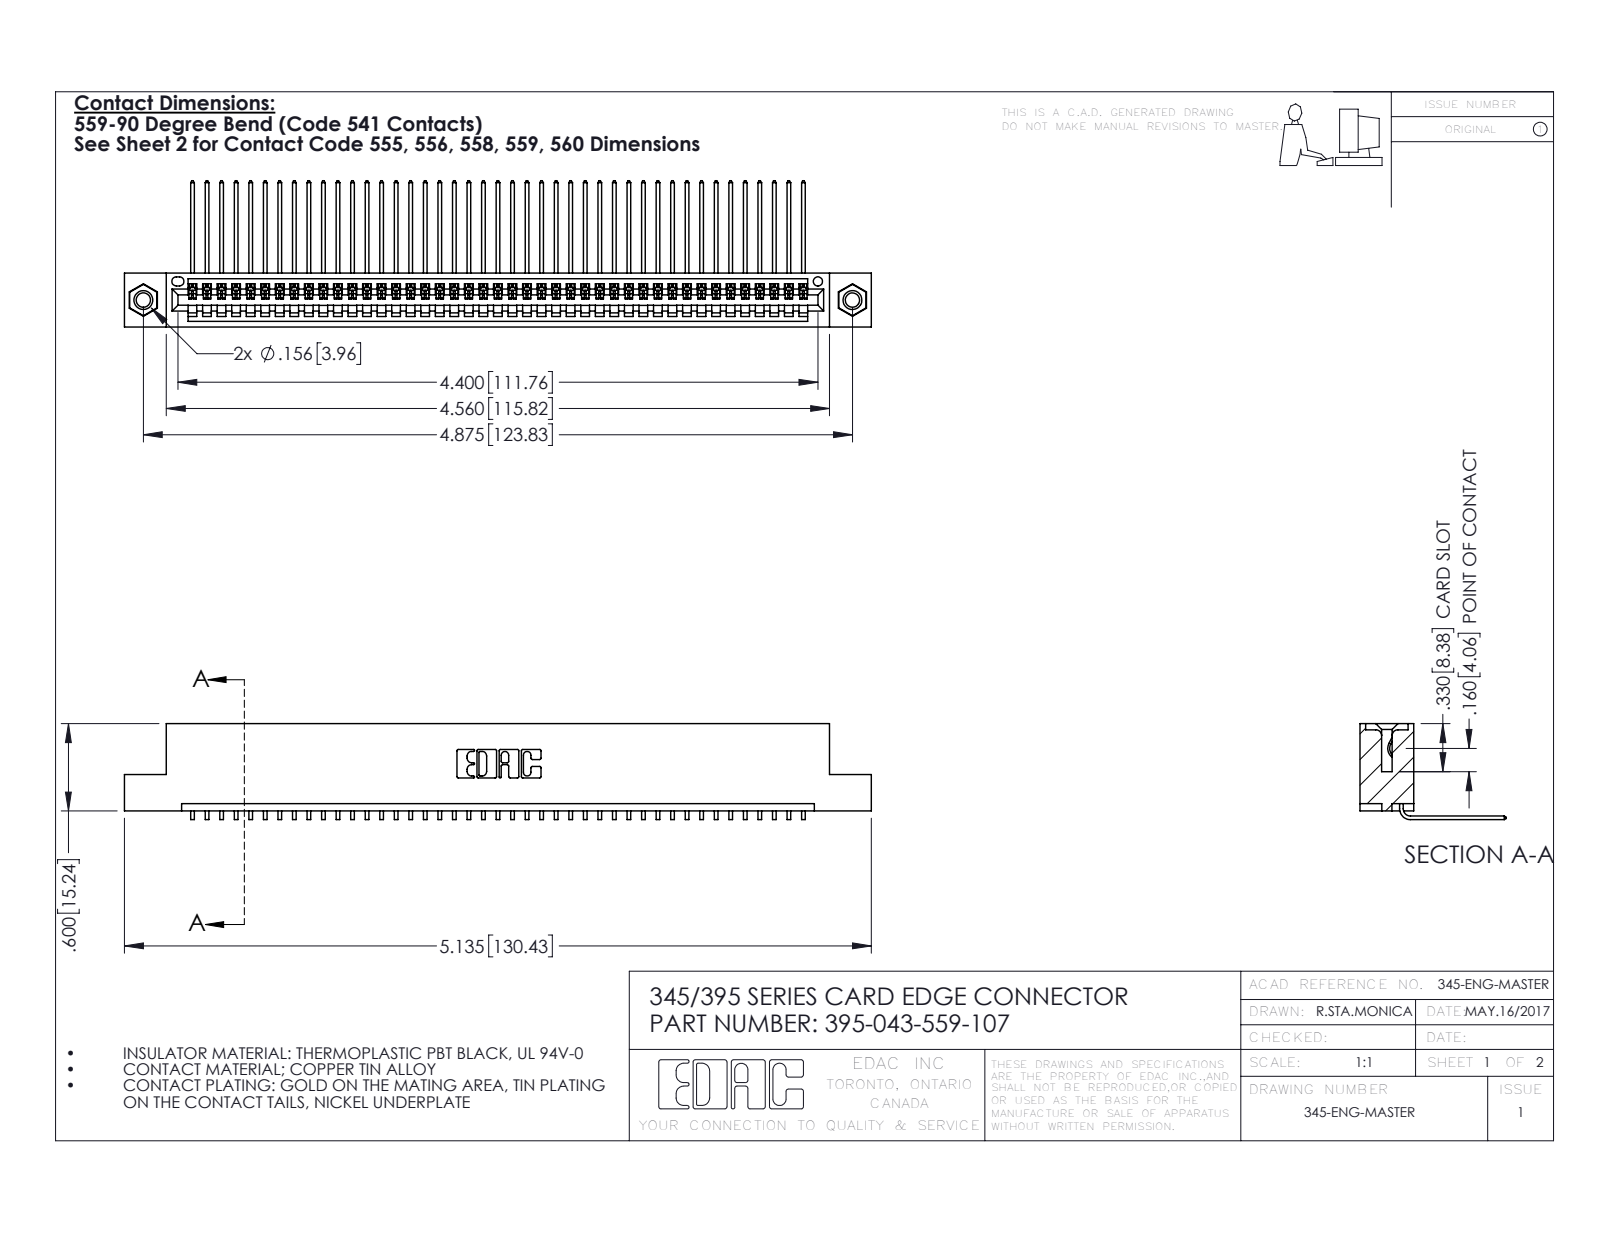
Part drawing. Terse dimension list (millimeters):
name: 345-250-001_345-250-005-103; 345-292-001_558 559 Tail - 1; 345 Part_Flush Mounting Lugs - 0.156 Dia-TI; 395-043-559-107
written by: SolidWorks 2016 (CONFIG_CONTROL_DESIGN)
unit: mm
bodies: 46 solids, 2766 faces (1918 planar, 832 cylindrical, 16 other)
size: 130.4 × 25.5 × 16.7
volume: 12 500 mm³; area: 17 540 mm²
holes: 2× ⌀2.5, 2× ⌀3.2, 2× ⌀4, 1× ⌀1.6
bosses: 2× ⌀3.9
rounds: 86× R0.2, 22× R0.3, 6× R0.2, 6× R0.8, 3× R0.7, 2× R0.8, 2× R1, 1× R0.4
face distances: 1.8, 7.6, 9.4, 5.1, 2.5, 6.9, 0.6, 5.7, 3.8, 1.8
hole spacings: 6.9, 117.8, 123.8
